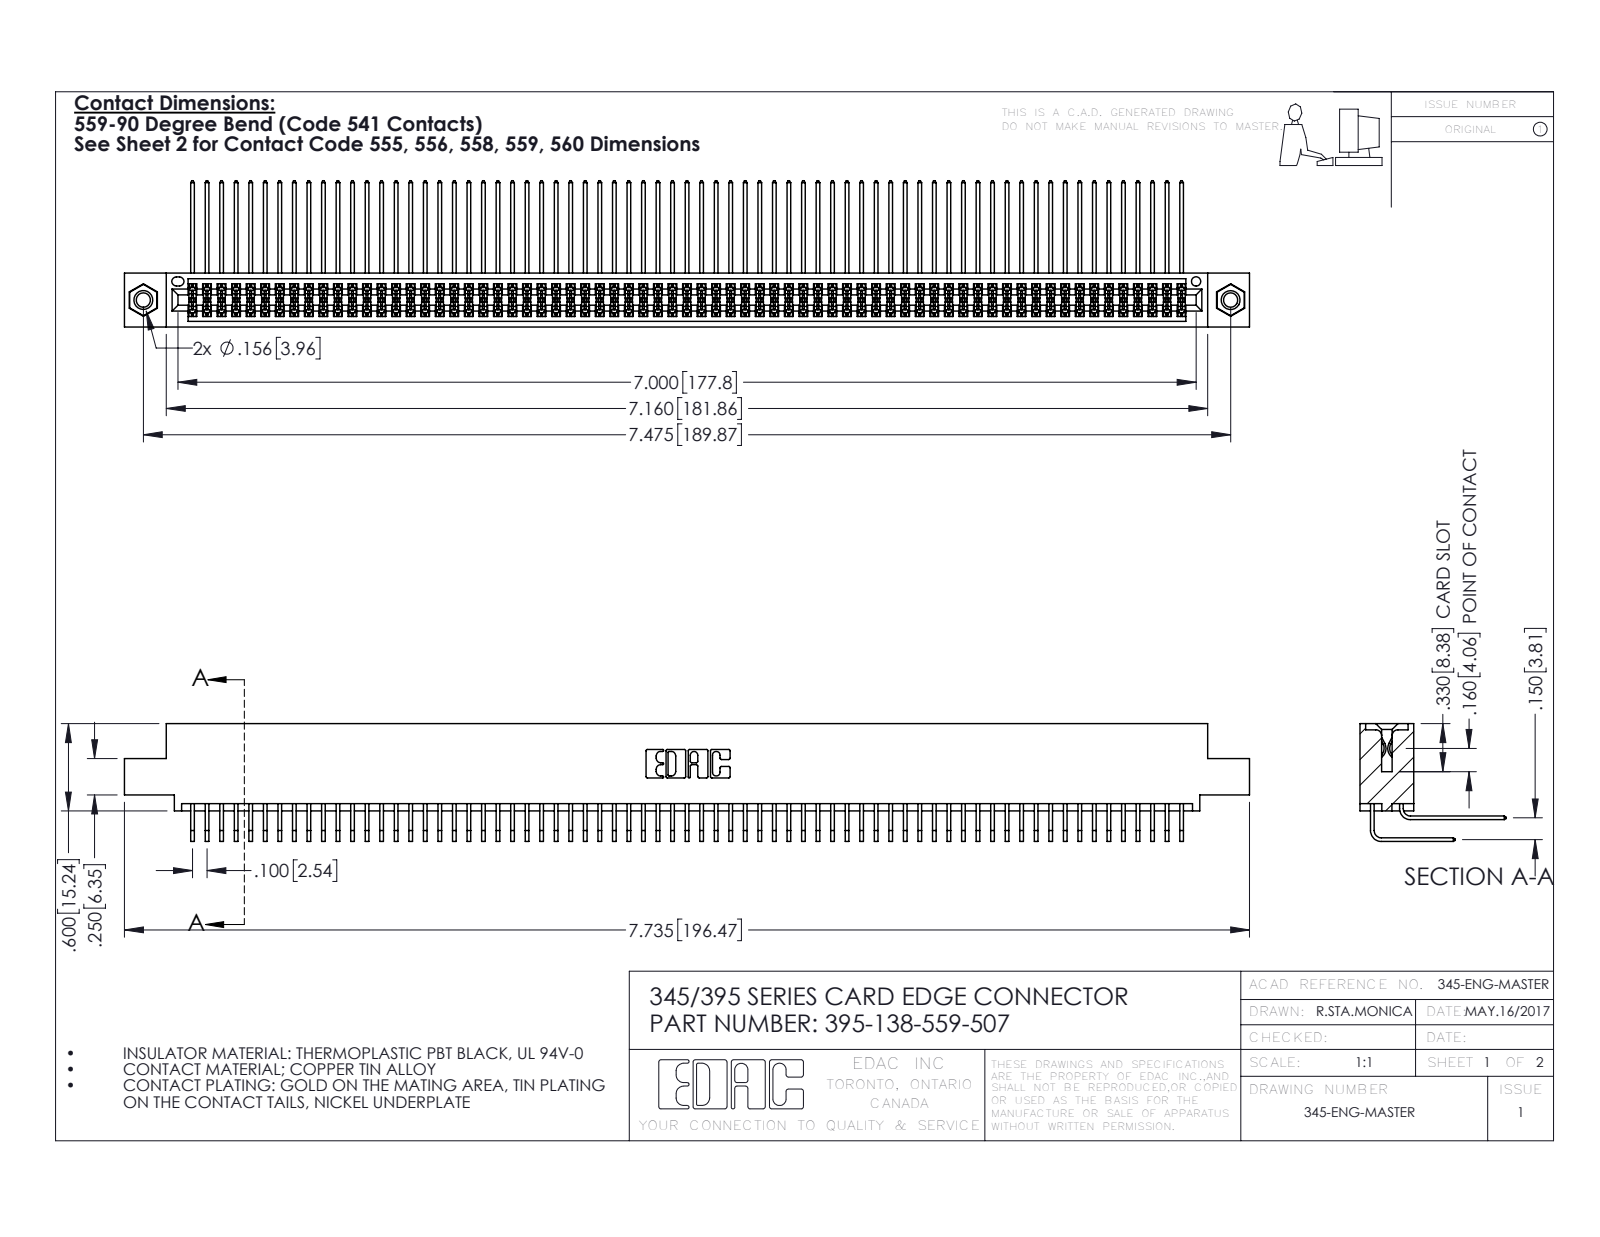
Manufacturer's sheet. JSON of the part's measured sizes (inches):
{"part_name": "345 Part_0.110 Offset - 0.156 Dia-TI; 395-138-559-507; 345-292-001_558 559 Tail - 1; 345-292-001_559 Tail - 2 (+1 more)", "step_written_by": "SolidWorks 2016 (CONFIG_CONTROL_DESIGN)", "units": "inches", "bodies": {"solids": 141, "faces": 7366, "planar": 4946, "cylindrical": 2404, "other": 16}, "overall_size": [7.735, 1.005, 0.809], "volume_in3": 1.223, "surface_area_in2": 52.73, "round_holes": [[0.098, 2], [0.125, 2], [0.156, 2], [0.064, 1]], "round_bosses_or_shafts": [[0.155, 2]], "partial_cylinders_radius": [[0.006, 275], [0.01, 22], [0.007, 6], [0.031, 6], [0.026, 3], [0.014, 2], [0.019, 2], [0.022, 2]], "face_to_face_distances": [0.072, 0.298, 0.2, 0.37, 0.098, 0.272, 0.025, 0.225, 0.175, 0.15], "hole_center_spacings": [0.27, 7.239, 7.475]}
